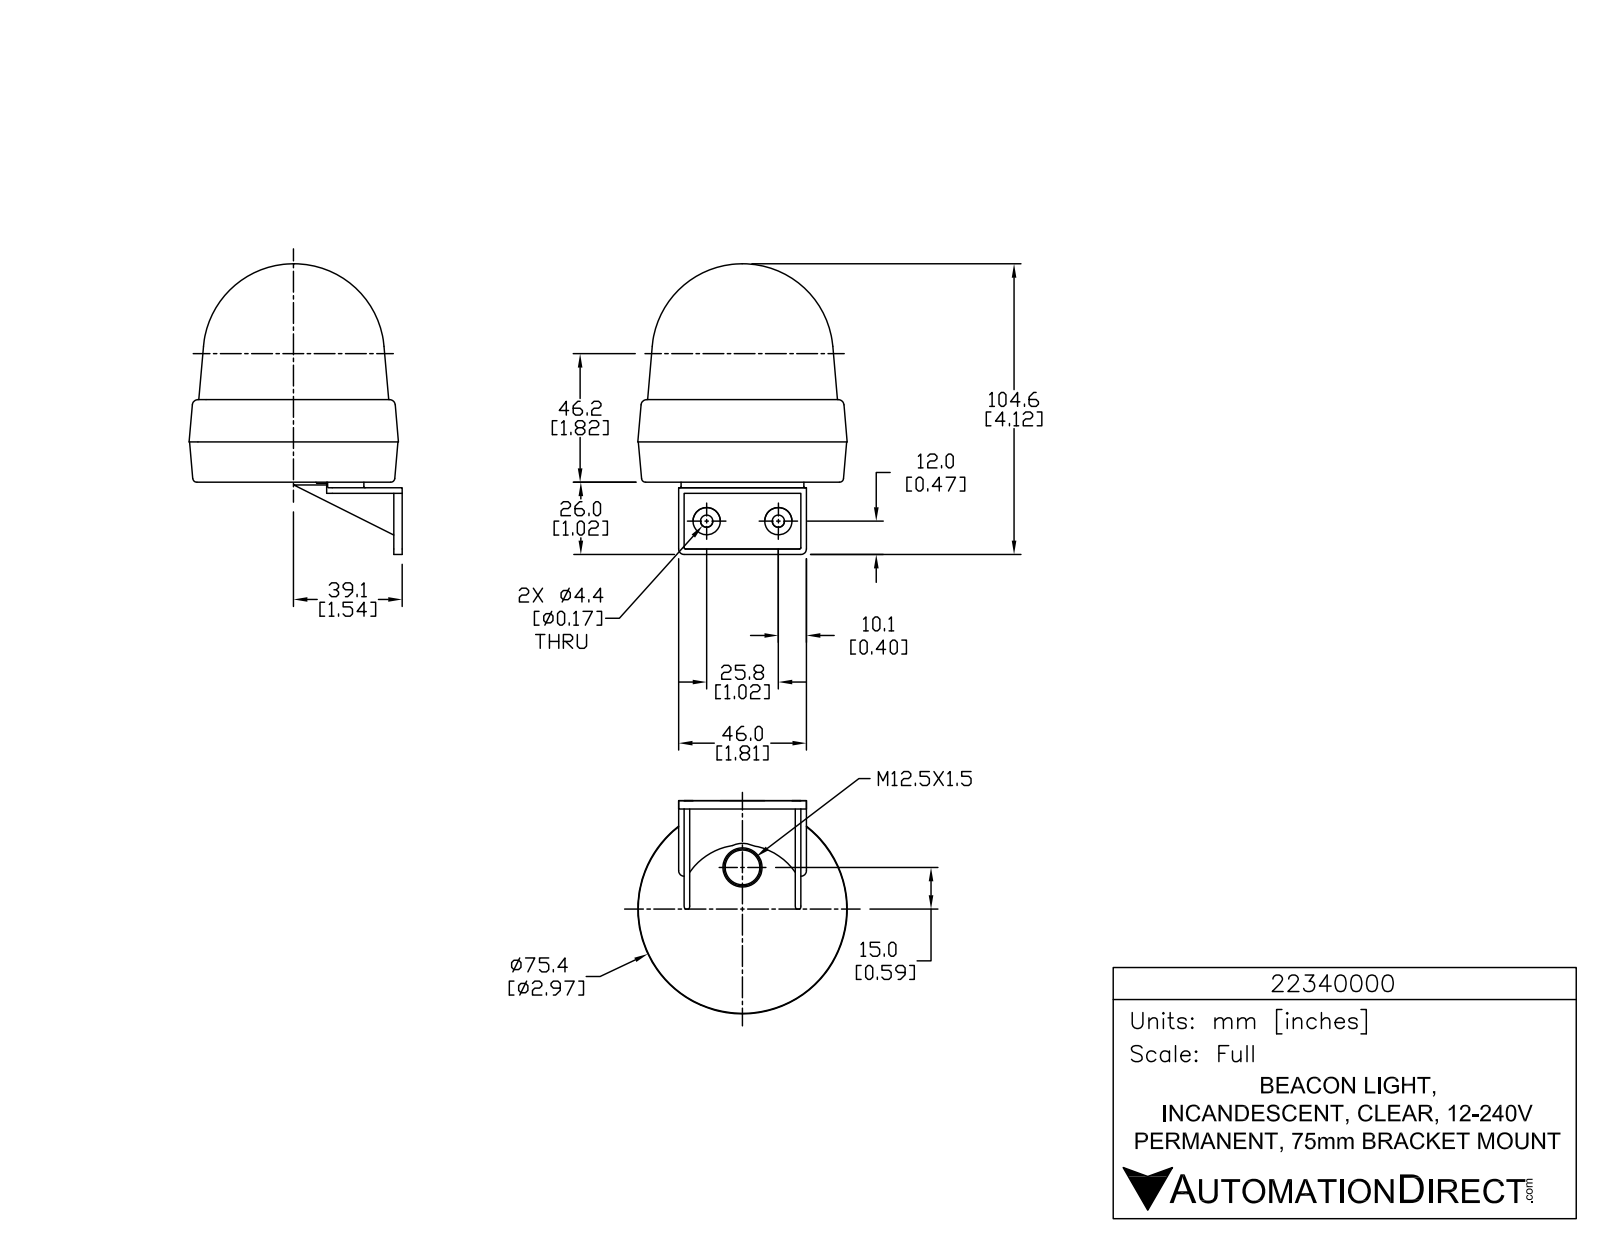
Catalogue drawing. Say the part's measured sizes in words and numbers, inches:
The part is named "22340000". Its 3-D file was written by "SolidWorks 2015 (AUTOMOTIVE_DESIGN)". It is 1 solid with 819 faces: 549 planar, 180 cylindrical and 90 other. Overall it measures 4.117 by 3.253 by 2.967 inches. Its volume is 16.02 cubic inches and its surface area 41.97 square inches. Round holes: 3 of diameter 0.059, 2 of diameter 0.173. Round bosses or shafts: 3 of diameter 0.339, 3 of diameter 0.084, 2 of diameter 0.386. Partial cylindrical surfaces (rounded edges, fillets, slot ends): 9 of radius 0.005, 6 of radius 0.005, 6 of radius 0.012, 6 of radius 0.012, 6 of radius 0.012, 6 of radius 0.02, 6 of radius 0.196, 4 of radius 0.079. The main face-to-face distances are 0.079, 0.157, 1.574, 0.039, 0.118, 1.653, 1.496, 0.079, 1.654, 1.732. The hole center spacings are 1.016.
